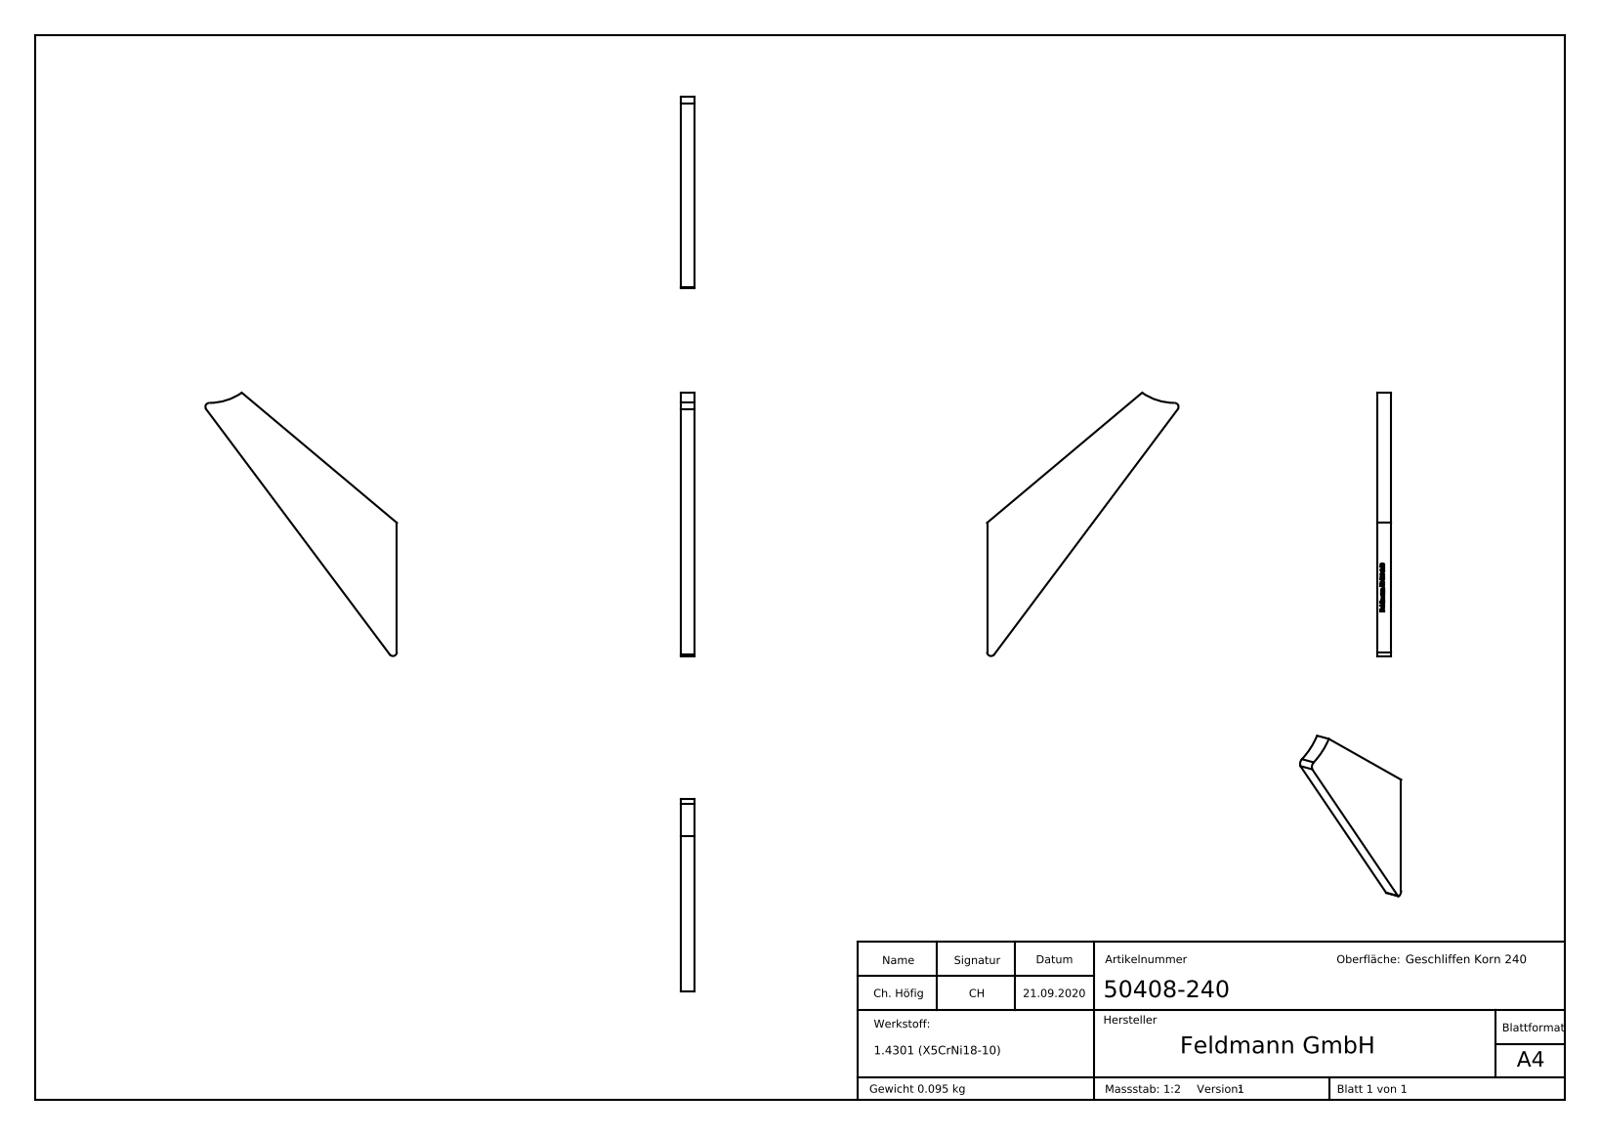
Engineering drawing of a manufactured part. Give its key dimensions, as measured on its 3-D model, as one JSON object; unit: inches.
{"part_name": "50408-240", "step_written_by": "SolidWorks 2018 (CONFIG_CONTROL_DESIGN)", "units": "inches", "bodies": {"solids": 1, "faces": 238, "planar": 128, "cylindrical": 4, "other": 106}, "overall_size": [3.892, 2.83, 0.197], "volume_in3": 0.734, "surface_area_in2": 9.484, "partial_cylinders_radius": [[0.059, 2], [0.835, 1]], "face_to_face_distances": [0.197, 0.098, 0.117, 0.015, 0.017, 0.152, 0.052, 0.035, 0.576, 0.342]}
